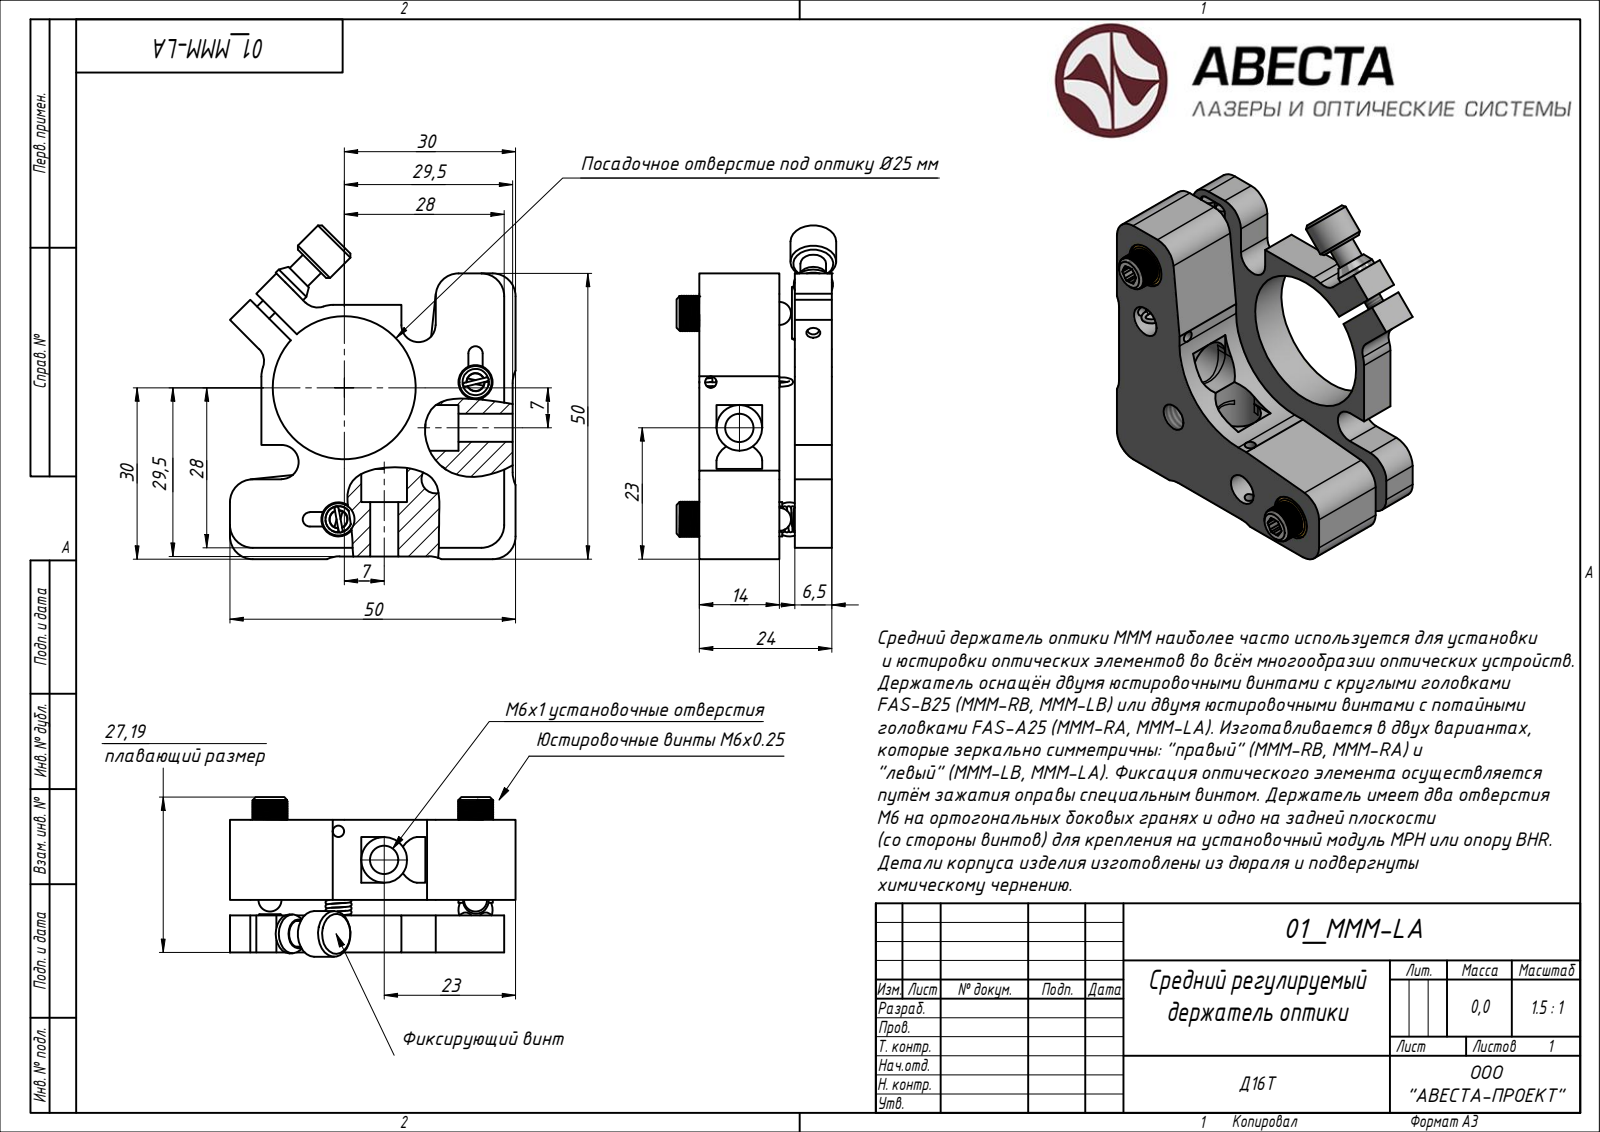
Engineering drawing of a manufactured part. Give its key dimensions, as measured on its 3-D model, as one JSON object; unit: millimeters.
{"step_written_by": "ST-DEVELOPER v15 (AUTOMOTIVE_DESIGN)", "units": "millimeters", "bodies": {"solids": 15, "faces": 332, "planar": 131, "cylindrical": 0, "other": 201}, "overall_size": [58.41, 50, 41.45], "volume_mm3": 26043, "surface_area_mm2": 16167, "face_to_face_distances": [6.5, 14, 9.98, 17.48, 23.98, 3.48, 2, 1.5, 0.5, 5.5]}
